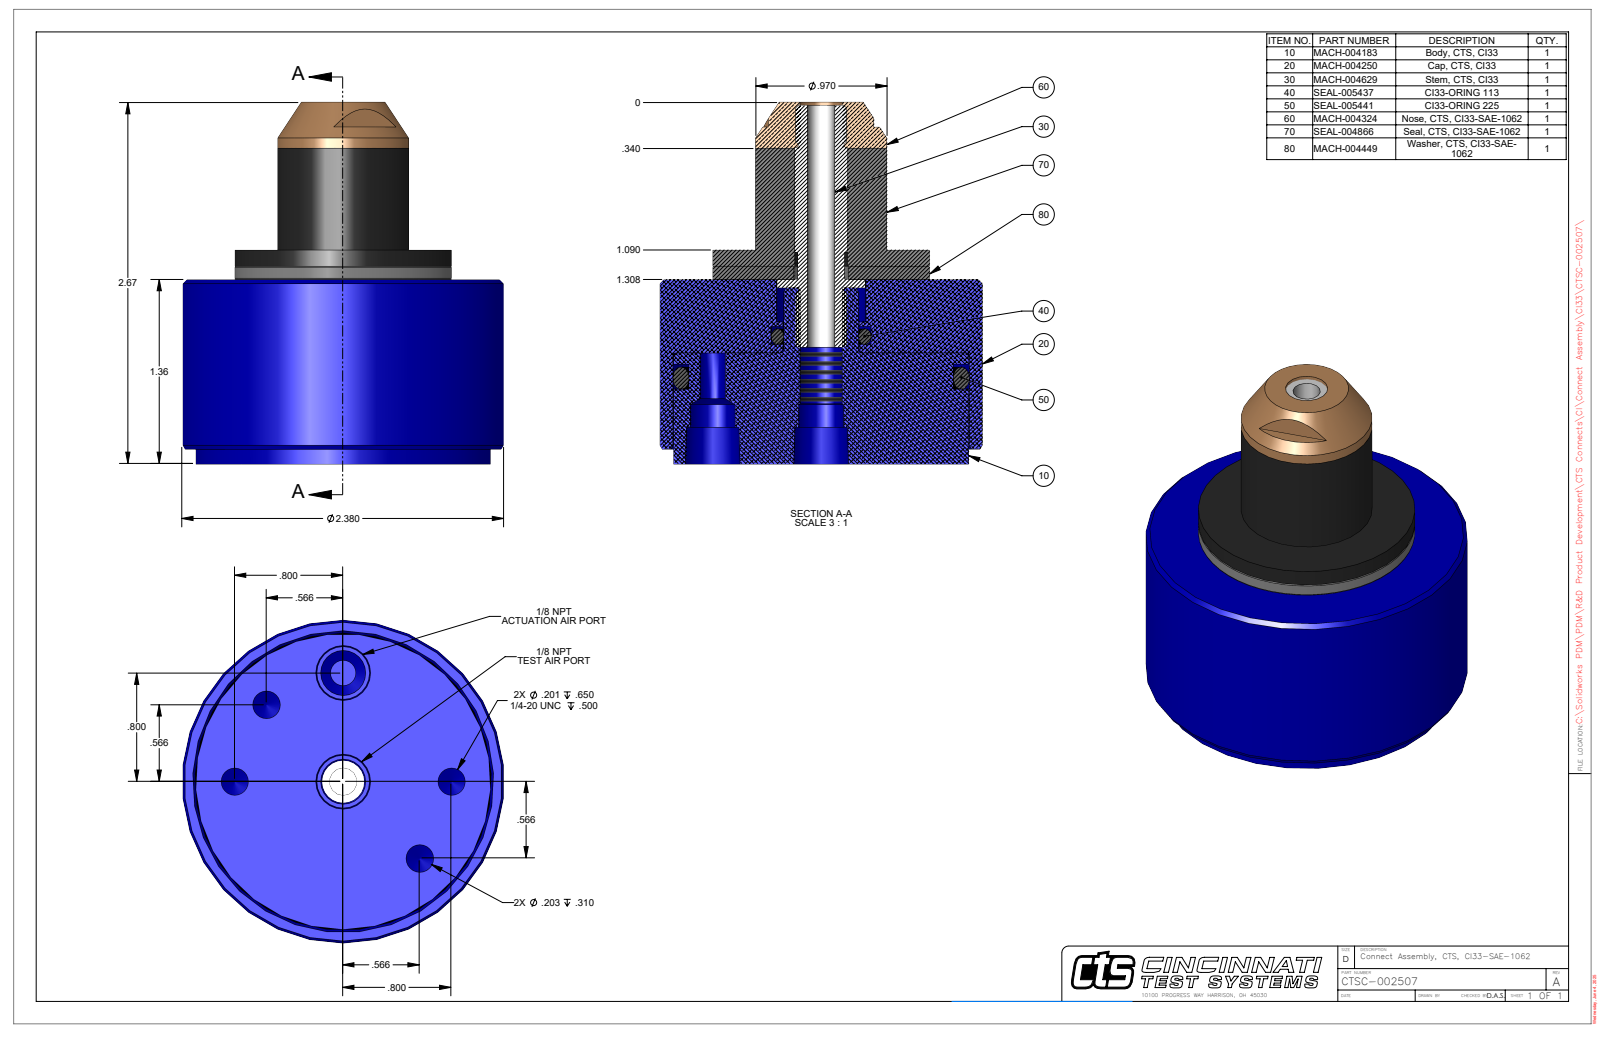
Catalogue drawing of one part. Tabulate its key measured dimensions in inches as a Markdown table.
| quantity | value |
| --- | --- |
| part name | CTSC-002507 |
| STEP written by | SolidWorks 2023 (AUTOMOTIVE_DESIGN) |
| units | inches |
| bodies | 1 solid, 76 faces (20 planar, 32 cylindrical, 24 other) |
| overall size | 2.668 × 2.38 × 2.38 |
| volume | 6.91 in³ |
| surface area | 30.91 in² |
| round holes (diameter × count) | 0.201 × 2, 0.203 × 2, 0.332 × 2, 0.203 × 1, 0.313 × 1, 0.659 × 1, 2.188 × 1 |
| round bosses / shafts (diameter × count) | 2.38 × 1, 2.178 × 1, 1.6 × 1, 0.97 × 1, 0.65 × 1 |
| main face-to-face distances | 1.36, 1.578, 0.218, 0.11, 1.25, 1.468, 2.668, 2.558, 1.308, 1.09 |
| hole center spacings | 0.8, 0.612, 1.478, 1.131, 1.6 |
